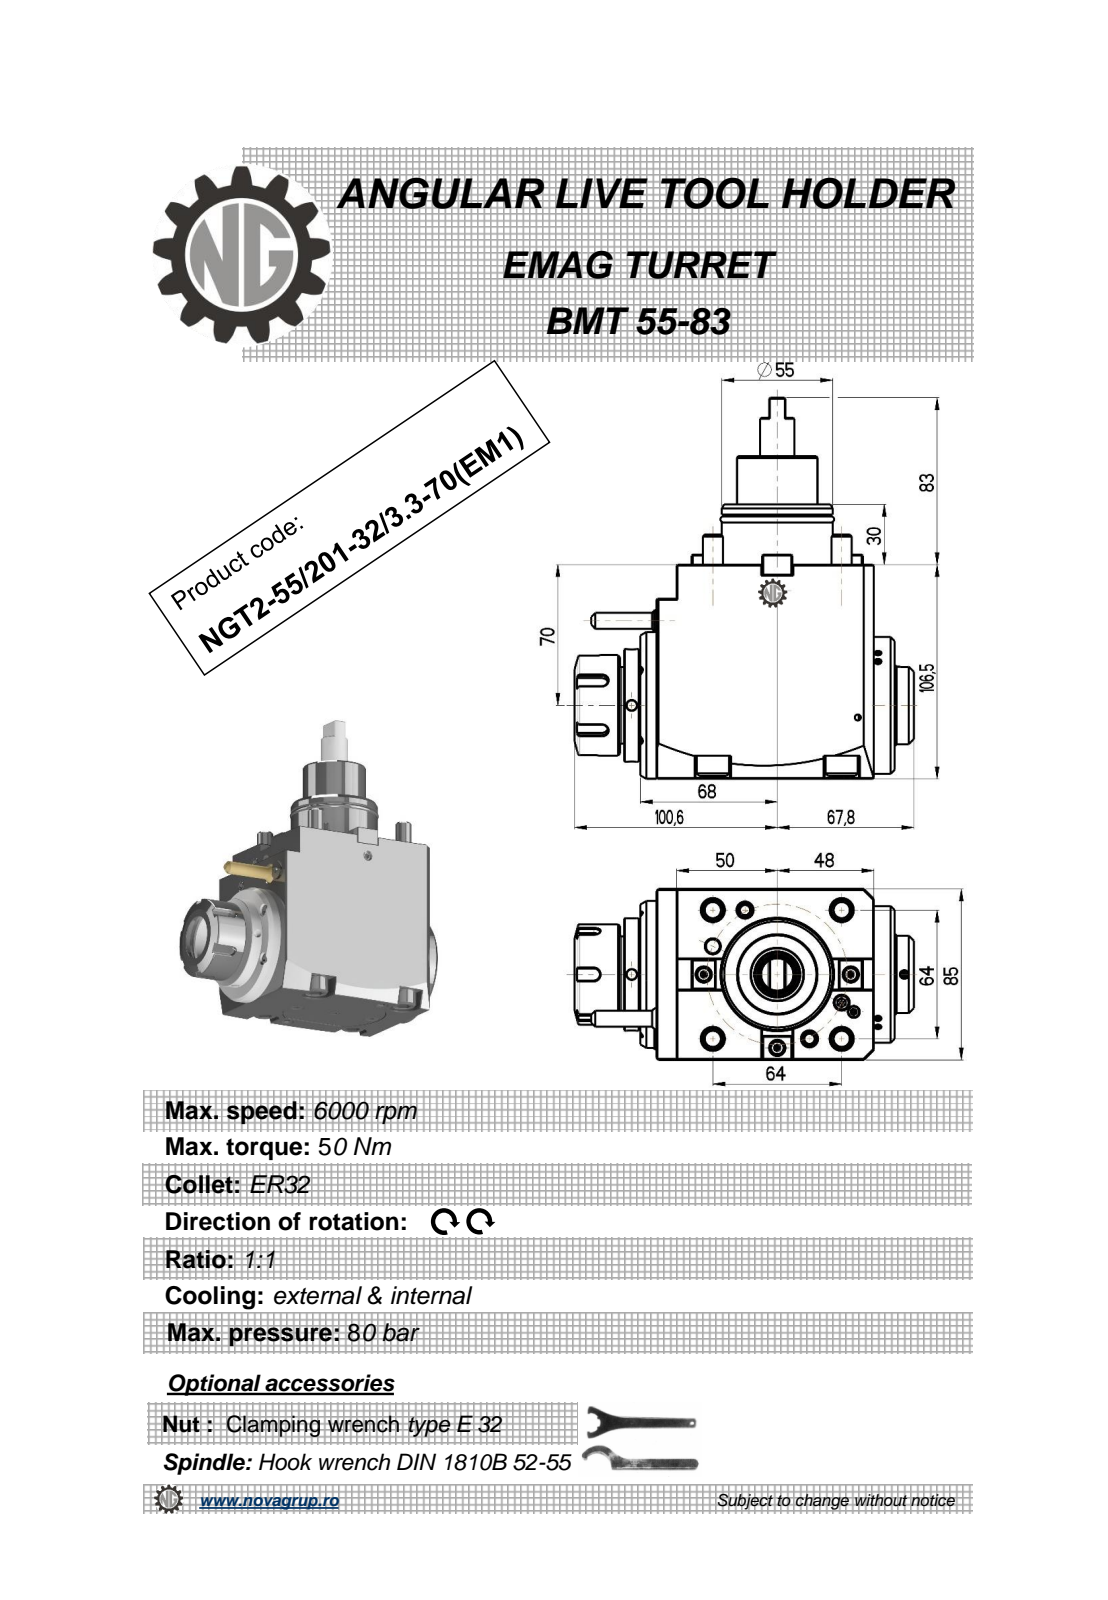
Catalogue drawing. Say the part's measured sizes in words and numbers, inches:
The part is named "NGT2_55_201_32_3_3_70_EM1". Its 3-D file was written by "PRO/ENGINEER BY PARAMETRIC TECHNOLOGY CORPORATION, 2010280 (CONFIG_CONTROL_DESIGN)". It is 2 solids with 479 faces: 229 planar, 113 cylindrical and 137 other. Overall it measures 7.461 by 6.63 by 3.346 inches. Its volume is 72.92 cubic inches and its surface area 163.1 square inches. Round holes: 3 of diameter 0.197, 2 of diameter 0.268, 1 of diameter 0.118, 1 of diameter 0.472, 1 of diameter 1.063. Round bosses or shafts: 4 of diameter 0.63, 4 of diameter 0.394, 2 of diameter 1.969, 1 of diameter 2.874, 1 of diameter 2.677, 1 of diameter 2.205, 1 of diameter 2.165, 1 of diameter 1.709. Partial cylindrical surfaces (rounded edges, fillets, slot ends): 20 of radius 0.013, 6 of radius 0.009, 5 of radius 0.118, 4 of radius 0.335, 2 of radius 0.031, 2 of radius 18.898. The main face-to-face distances are 3.346, 4.193, 0.315, 4.252, 4.567, 0.394, 0.709, 4.972, 4.657, 0.406. The hole center spacings are 1.678, 1.867, 2.75, 4.141.
